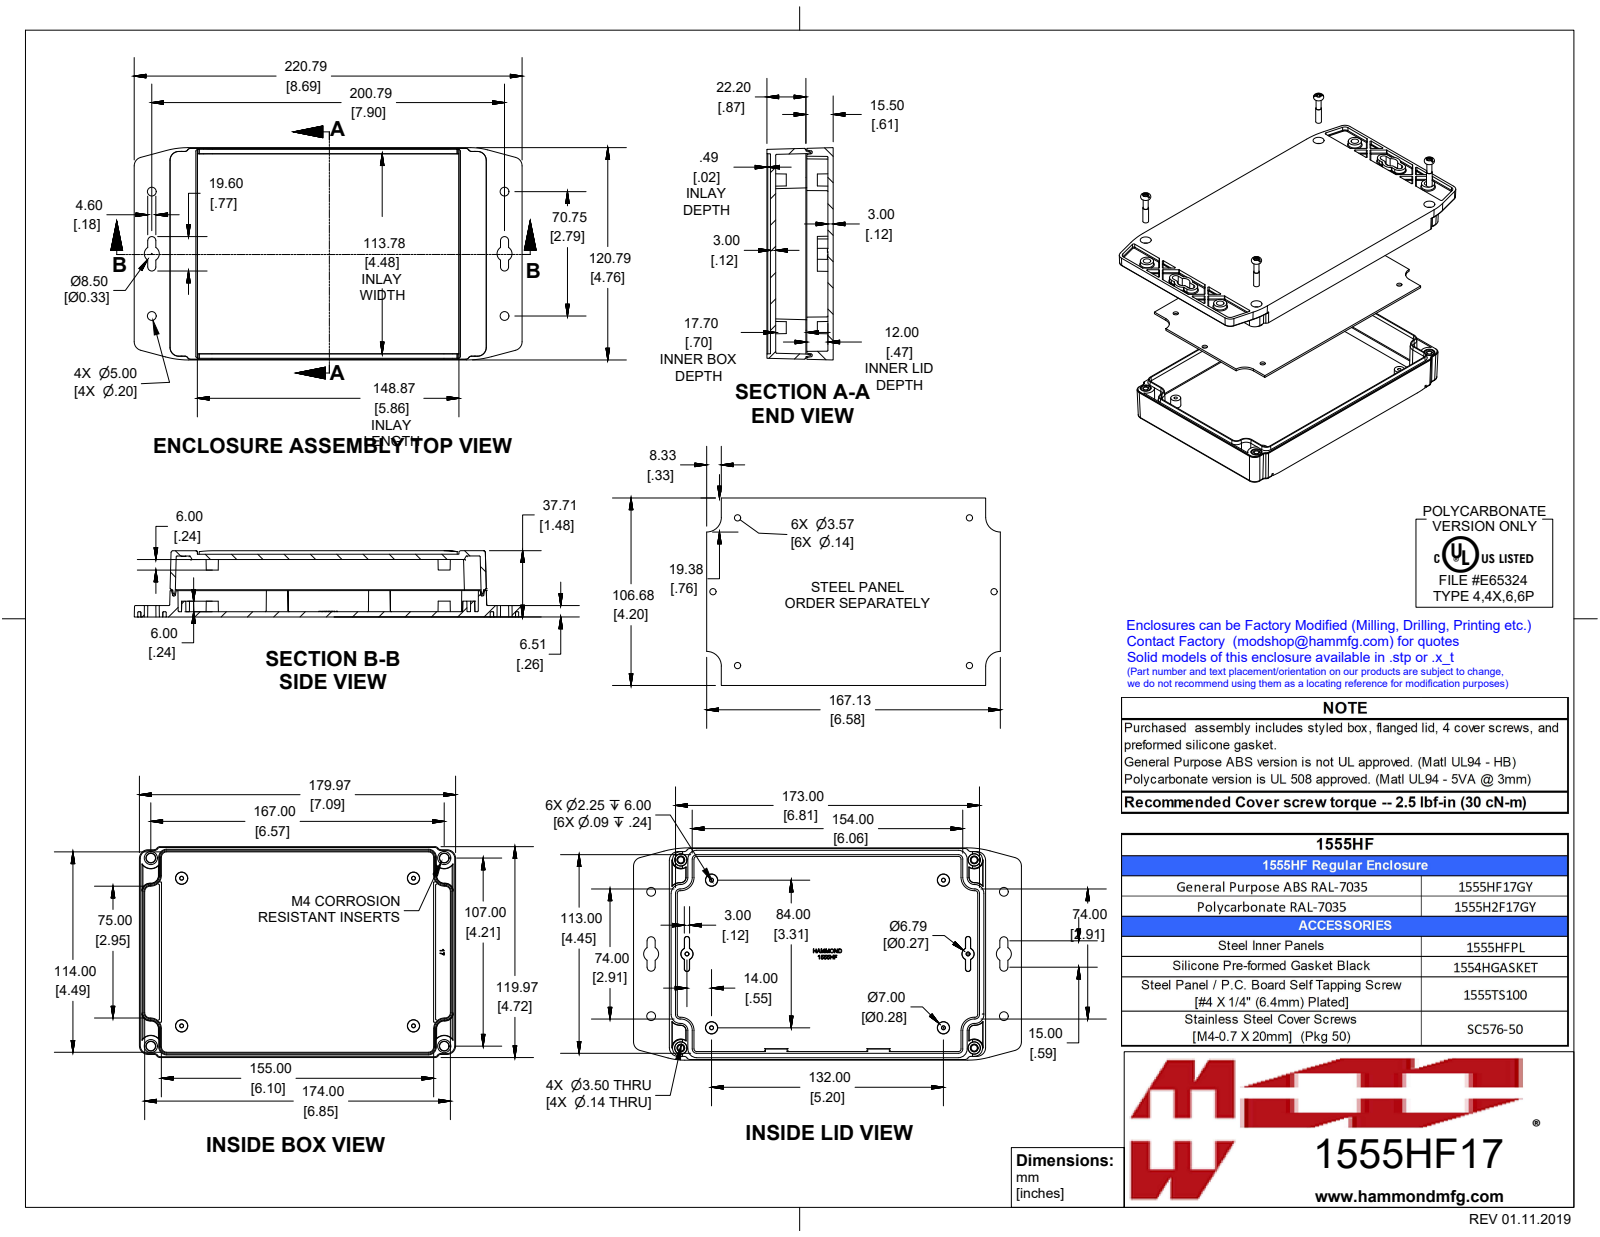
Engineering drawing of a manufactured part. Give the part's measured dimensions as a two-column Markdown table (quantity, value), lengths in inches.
| quantity | value |
| --- | --- |
| part name | 1555HF17GY |
| STEP written by | SolidWorks 2019 (CONFIG_CONTROL_DESIGN) |
| units | inches |
| bodies | 11 solids, 1328 faces (578 planar, 297 cylindrical, 453 other) |
| overall size | 8.692 × 4.755 × 1.484 |
| volume | 15.3 in³ |
| surface area | 294 in² |
| round holes (diameter × count) | 0.141 × 6, 0.128 × 4, 0.138 × 4, 0.295 × 4 |
| round bosses / shafts (diameter × count) | 0.354 × 4, 0.25 × 4, 0.218 × 4, 0.21 × 4, 0.153 × 4, 0.135 × 4 |
| partial cylindrical surfaces (radius × count) | 0.02 × 141, 0.197 × 12, 0.039 × 10, 0.089 × 4, 0.138 × 4, 0.169 × 4, 0.187 × 4, 0.328 × 4 |
| main face-to-face distances | 0.118, 1.287, 0.236, 0.354, 0.933, 1.169, 1.406, 0.411, 0.293, 0.057 |
| hole center spacings | 0.824, 1.743, 2.111, 3.822, 5.903, 5.981, 6.773, 6.984 |
